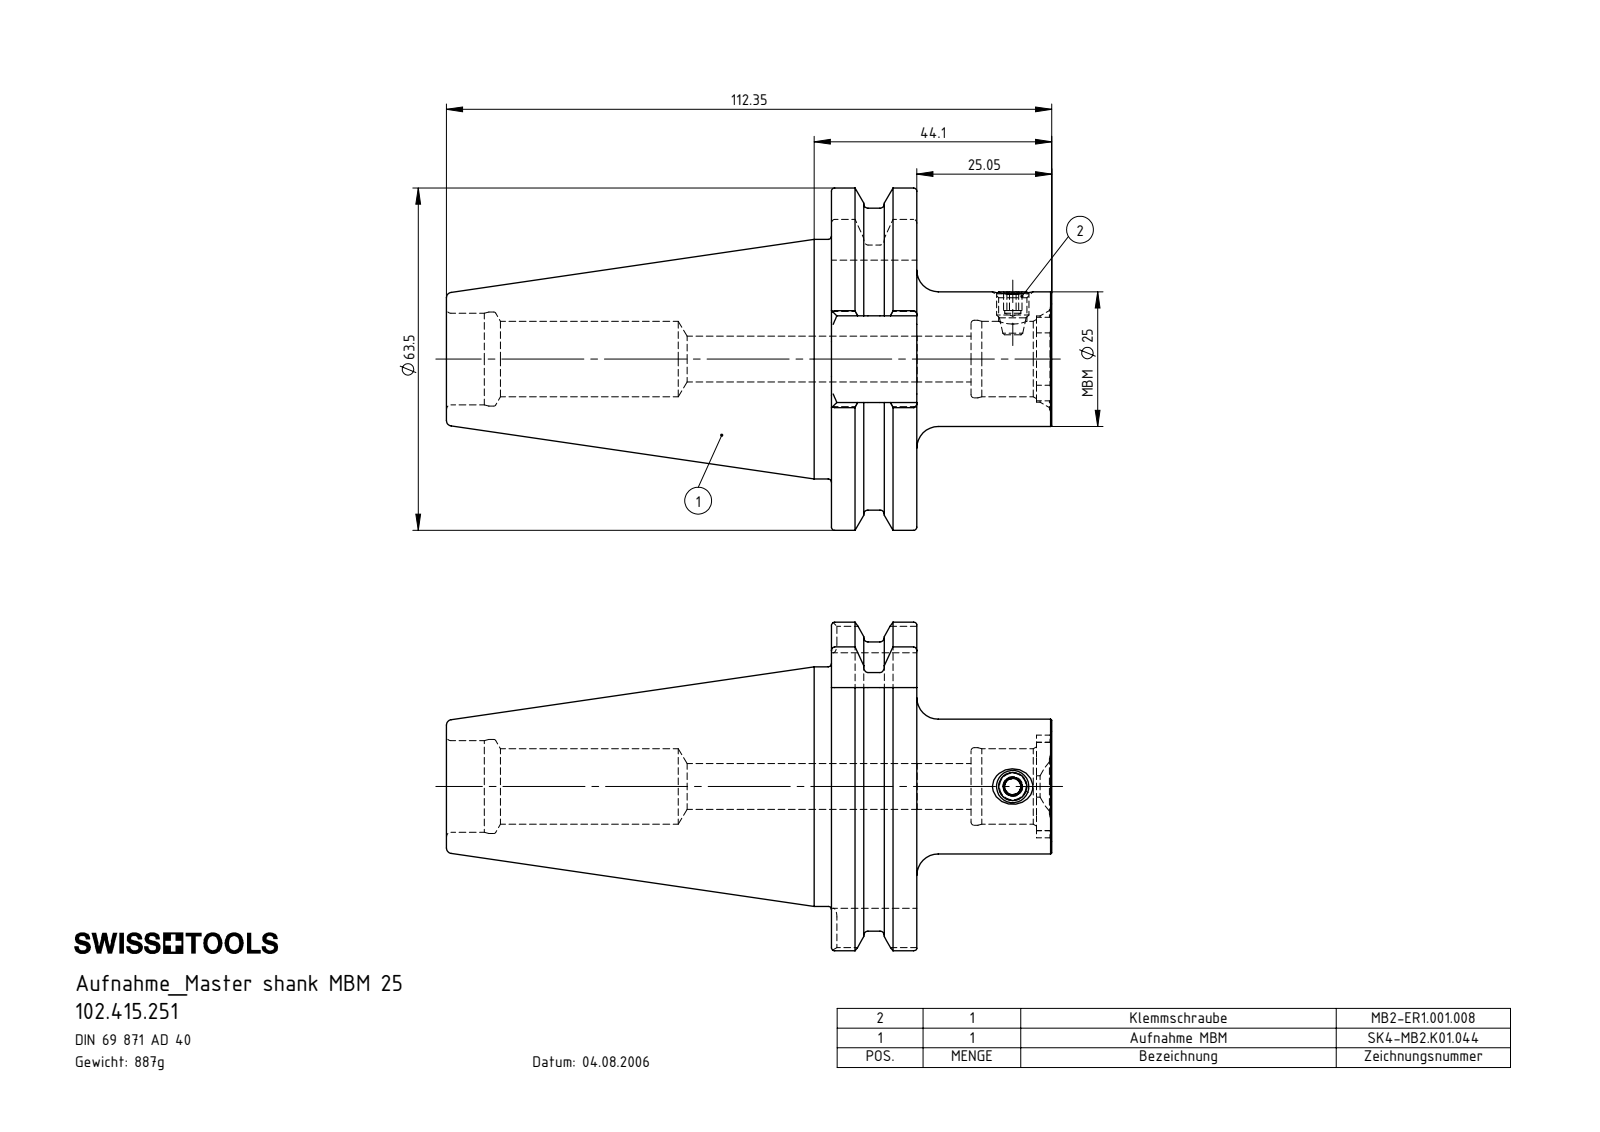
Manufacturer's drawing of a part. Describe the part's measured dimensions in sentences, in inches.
The part is named "102.415.251; MB2-ER1.001.008_A; SK4-MB2.K01.044_C". Its 3-D file was written by "SolidWorks 2017 (CONFIG_CONTROL_DESIGN)". It is 2 solids with 174 faces: 54 planar, 52 cylindrical and 68 other. Overall it measures 4.423 by 2.5 by 2.399 inches. Its volume is 6.892 cubic inches and its surface area 34.91 square inches. Round holes: 1 of diameter 0.118, 1 of diameter 0.207, 1 of diameter 0.335, 1 of diameter 0.551, 1 of diameter 0.567, 1 of diameter 0.669, 1 of diameter 0.687. Round bosses or shafts: 1 of diameter 1.75, 1 of diameter 0.984, 1 of diameter 0.236. Partial cylindrical surfaces (rounded edges, fillets, slot ends): 8 of radius 0.063, 4 of radius 0.106, 1 of radius 0.315, 1 of radius 0.375, 1 of radius 1.102, 1 of radius 1.25. The main face-to-face distances are 0.624, 1.866, 1.61, 0.986, 2.813, 3.437, 4.423, 0.634, 4.311, 1.498.
